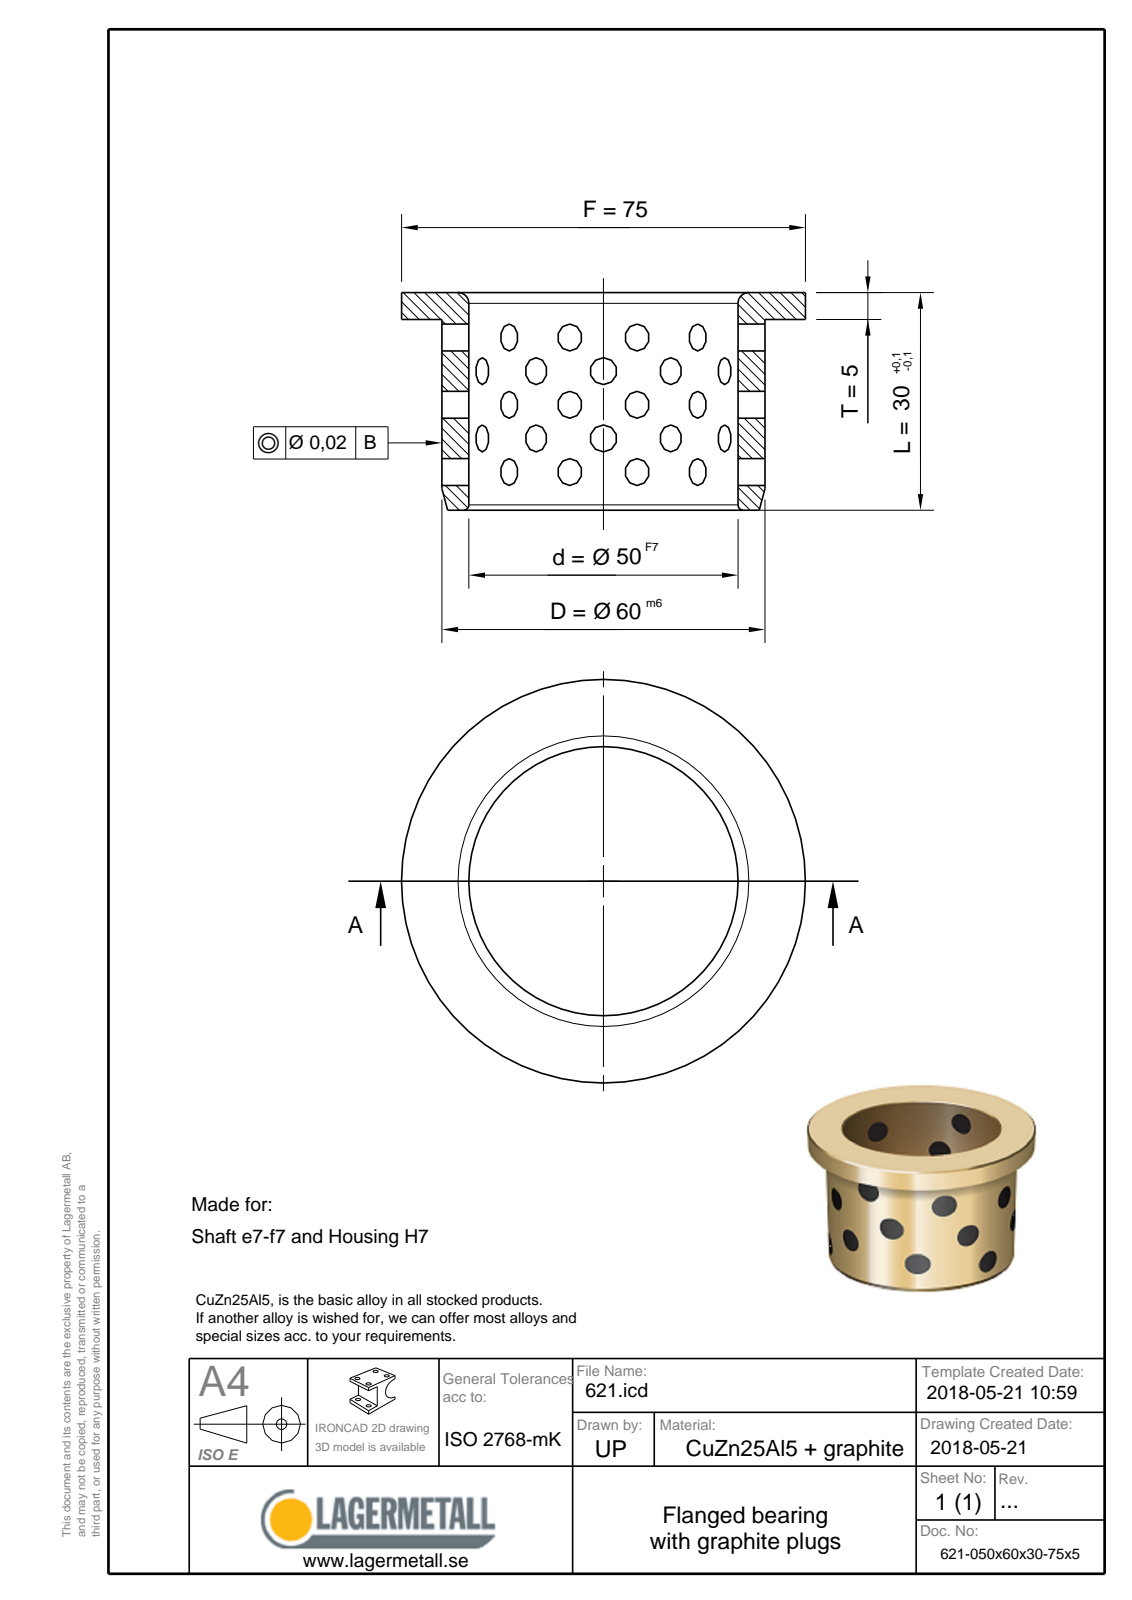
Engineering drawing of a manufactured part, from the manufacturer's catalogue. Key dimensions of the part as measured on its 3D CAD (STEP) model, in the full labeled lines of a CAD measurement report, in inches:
Part name (STEP PRODUCT): 621-050x60x30-75x5
STEP written by: Spatial InterOp 3D (CONFIG_CONTROL_DESIGN)
Units: inches
Bodies: 1 solid, 9 faces (3 planar, 3 cylindrical, 3 other)
Overall size (bounding box): 2.953 × 2.953 × 1.181
Volume: 2.037 in³ · Surface area: 23.42 in²
Round holes (diameter × count): ⌀1.969 ×1
Round bosses / shafts (diameter × count): ⌀2.953 ×1, ⌀2.362 ×1
Main face-to-face distances: 0.197, 0.984, 1.181
